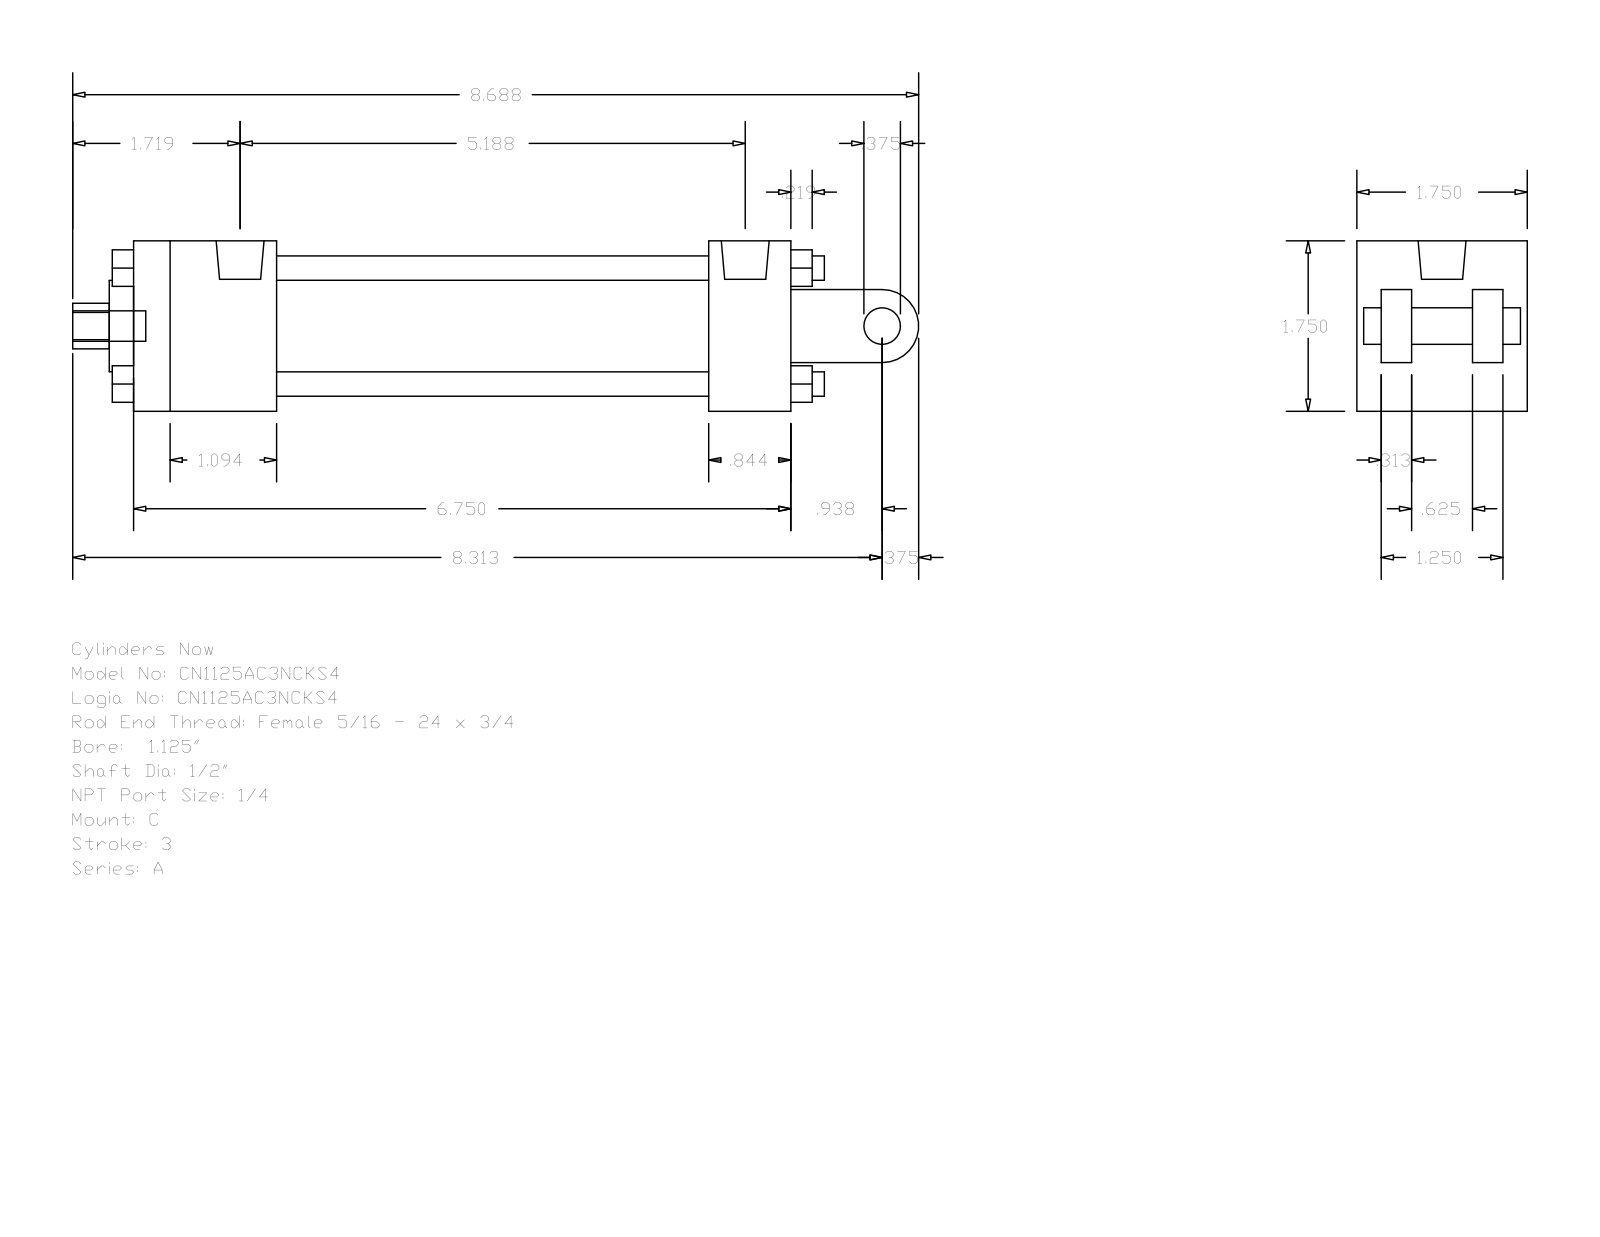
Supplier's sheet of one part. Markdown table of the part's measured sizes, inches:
| quantity | value |
| --- | --- |
| part name | A_C__0112_0.5 |
| STEP written by | GSSL Pune (CONFIG_CONTROL_DESIGN) |
| units | inches |
| bodies | 0 solids, 135 faces (102 planar, 33 cylindrical, 0 other) |
| overall size | 8.687 × 1.75 × 1.75 |
| round holes (diameter × count) | 0.219 × 2, 0.492 × 1, 0.5 × 1, 0.937 × 1, 1.255 × 1 |
| round bosses / shafts (diameter × count) | 0.25 × 4, 0.219 × 2, 0.492 × 1, 0.375 × 1, 0.313 × 1 |
| partial cylindrical surfaces (radius × count) | 0.234 × 1, 0.375 × 1 |
| main face-to-face distances | 1.75, 0.25, 1.25, 0.563, 6.75, 1.188, 5.906, 0.844, 1.469, 4.437 |
| hole center spacings | 0.063 |
